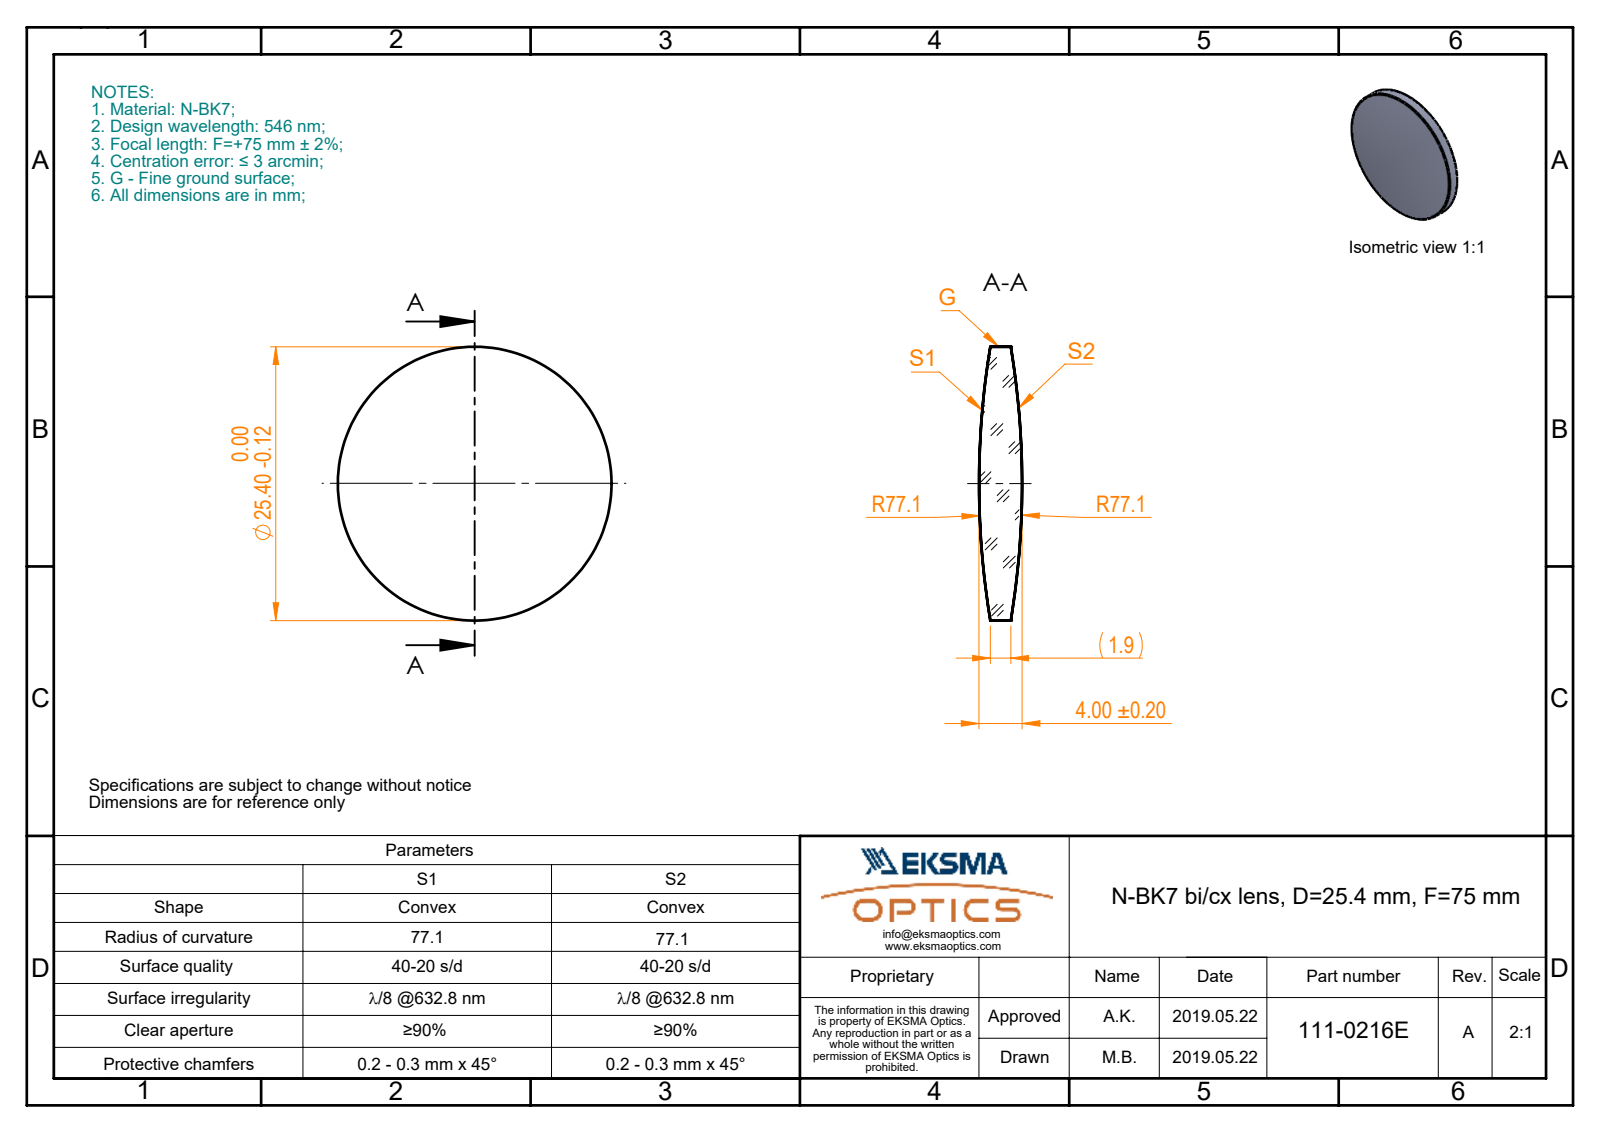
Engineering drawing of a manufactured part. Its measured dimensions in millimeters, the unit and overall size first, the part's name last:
Units: millimetres
Overall size (bounding box): 25.4 × 25.4 × 4
Round bosses / shafts (diameter × count): ⌀25.4 ×1
Volume: 1 495 mm³ · Surface area: 1 172 mm²
Bodies: 1 solid, 6 faces (0 planar, 2 cylindrical, 4 other)
Part name (STEP PRODUCT): 111-0216E BK7 bi-cx 25.4 F75
STEP written by: SolidWorks 2017 (CONFIG_CONTROL_DESIGN)
